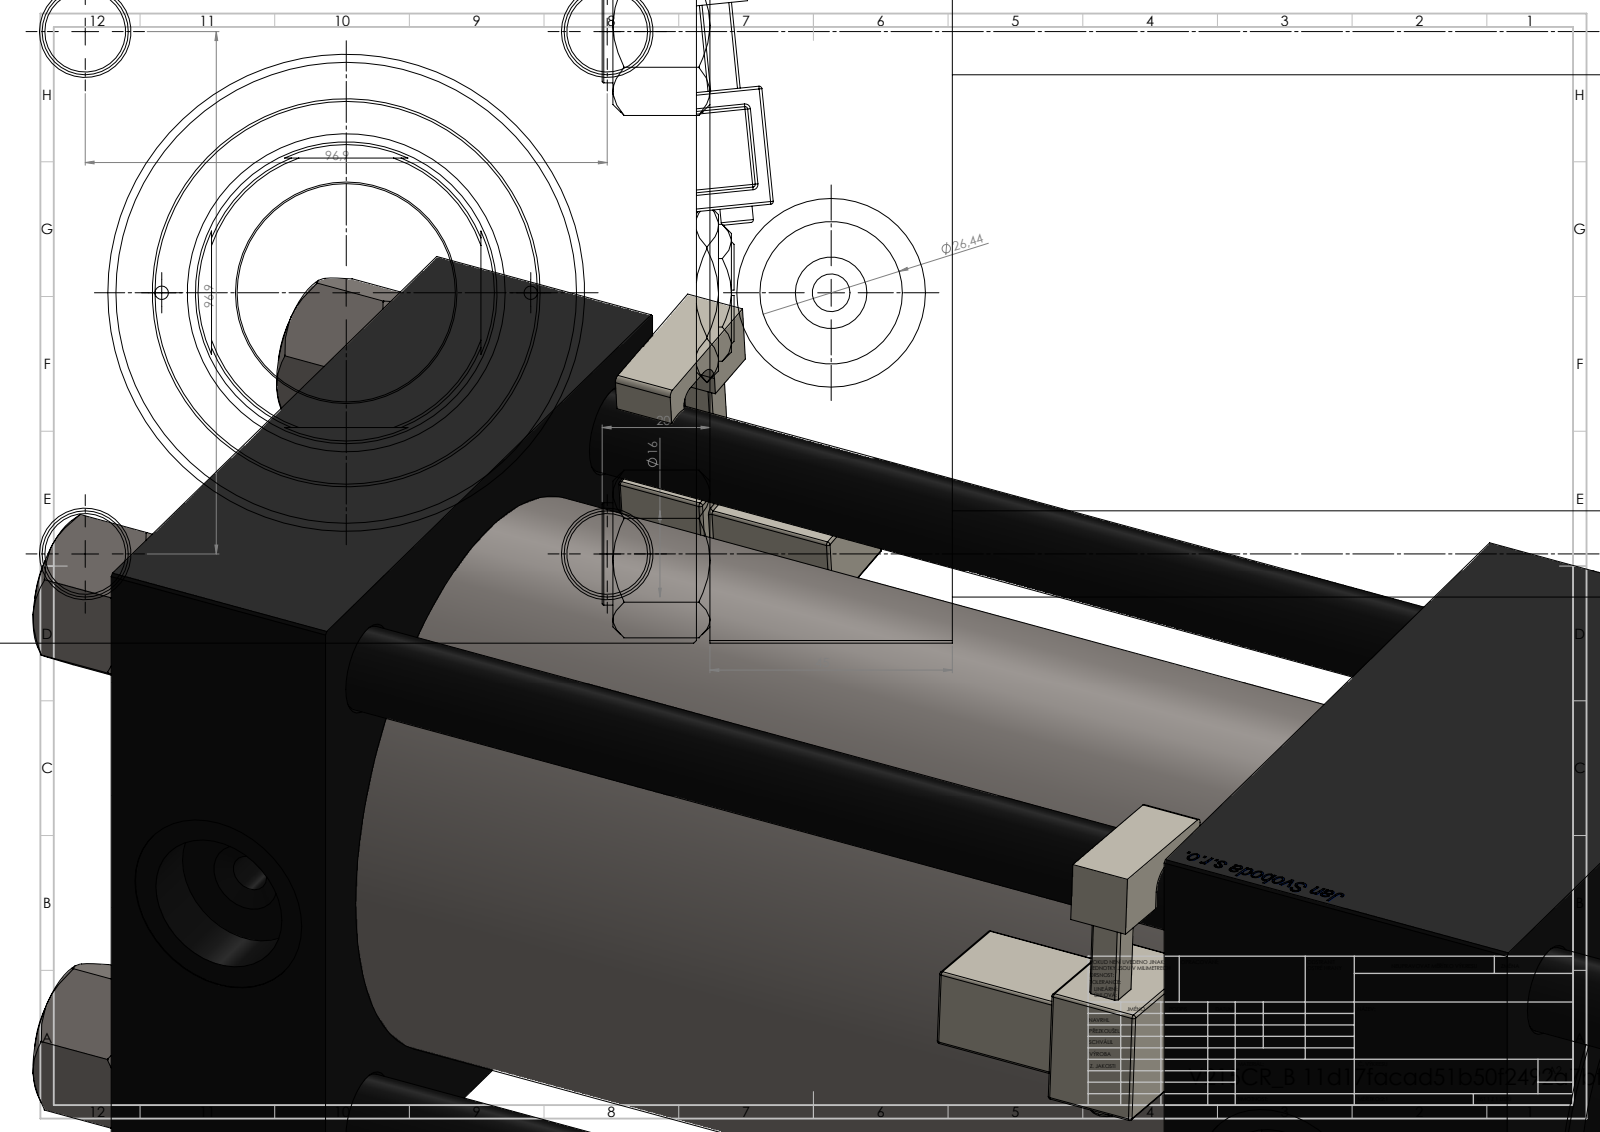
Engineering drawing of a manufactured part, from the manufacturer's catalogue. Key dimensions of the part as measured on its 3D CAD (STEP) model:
Part name (STEP PRODUCT): Zatka_pro_OIL_PORT; V215CR_VCP_B; V215_VC_A; V215CR_B-1 (+3 more)
STEP written by: SolidWorks 2019 (CONFIG_CONTROL_DESIGN)
Units: millimetres
Bodies: 14 solids, 1418 faces (564 planar, 148 cylindrical, 706 other)
Overall size (bounding box): 372 × 157.53 × 130.63
Volume: 3 038 000 mm³ · Surface area: 484 372 mm²
Round holes (diameter × count): ⌀16 ×4, ⌀2.5 ×2, ⌀7 ×2, ⌀26.44 ×2, ⌀35 ×2, ⌀40.5 ×1, ⌀56 ×1, ⌀59 ×1, ⌀76 ×1, ⌀85.5 ×1, ⌀100 ×1
Round bosses / shafts (diameter × count): ⌀19 ×4, ⌀6 ×2, ⌀106 ×1, ⌀72 ×1
Partial cylindrical surfaces — rounded edges, fillets, slot ends (radius × count): R0.5 ×48, R1 ×2, R2.5 ×2, R4 ×2, R27 ×1
Main face-to-face distances: 130, 45, 293, 248, 221, 176, 72, 51, 96, 125
Hole centre spacings: 50.49, 68.52, 95.85, 96.9, 34.25, 137.04, 68.5, 223.5
